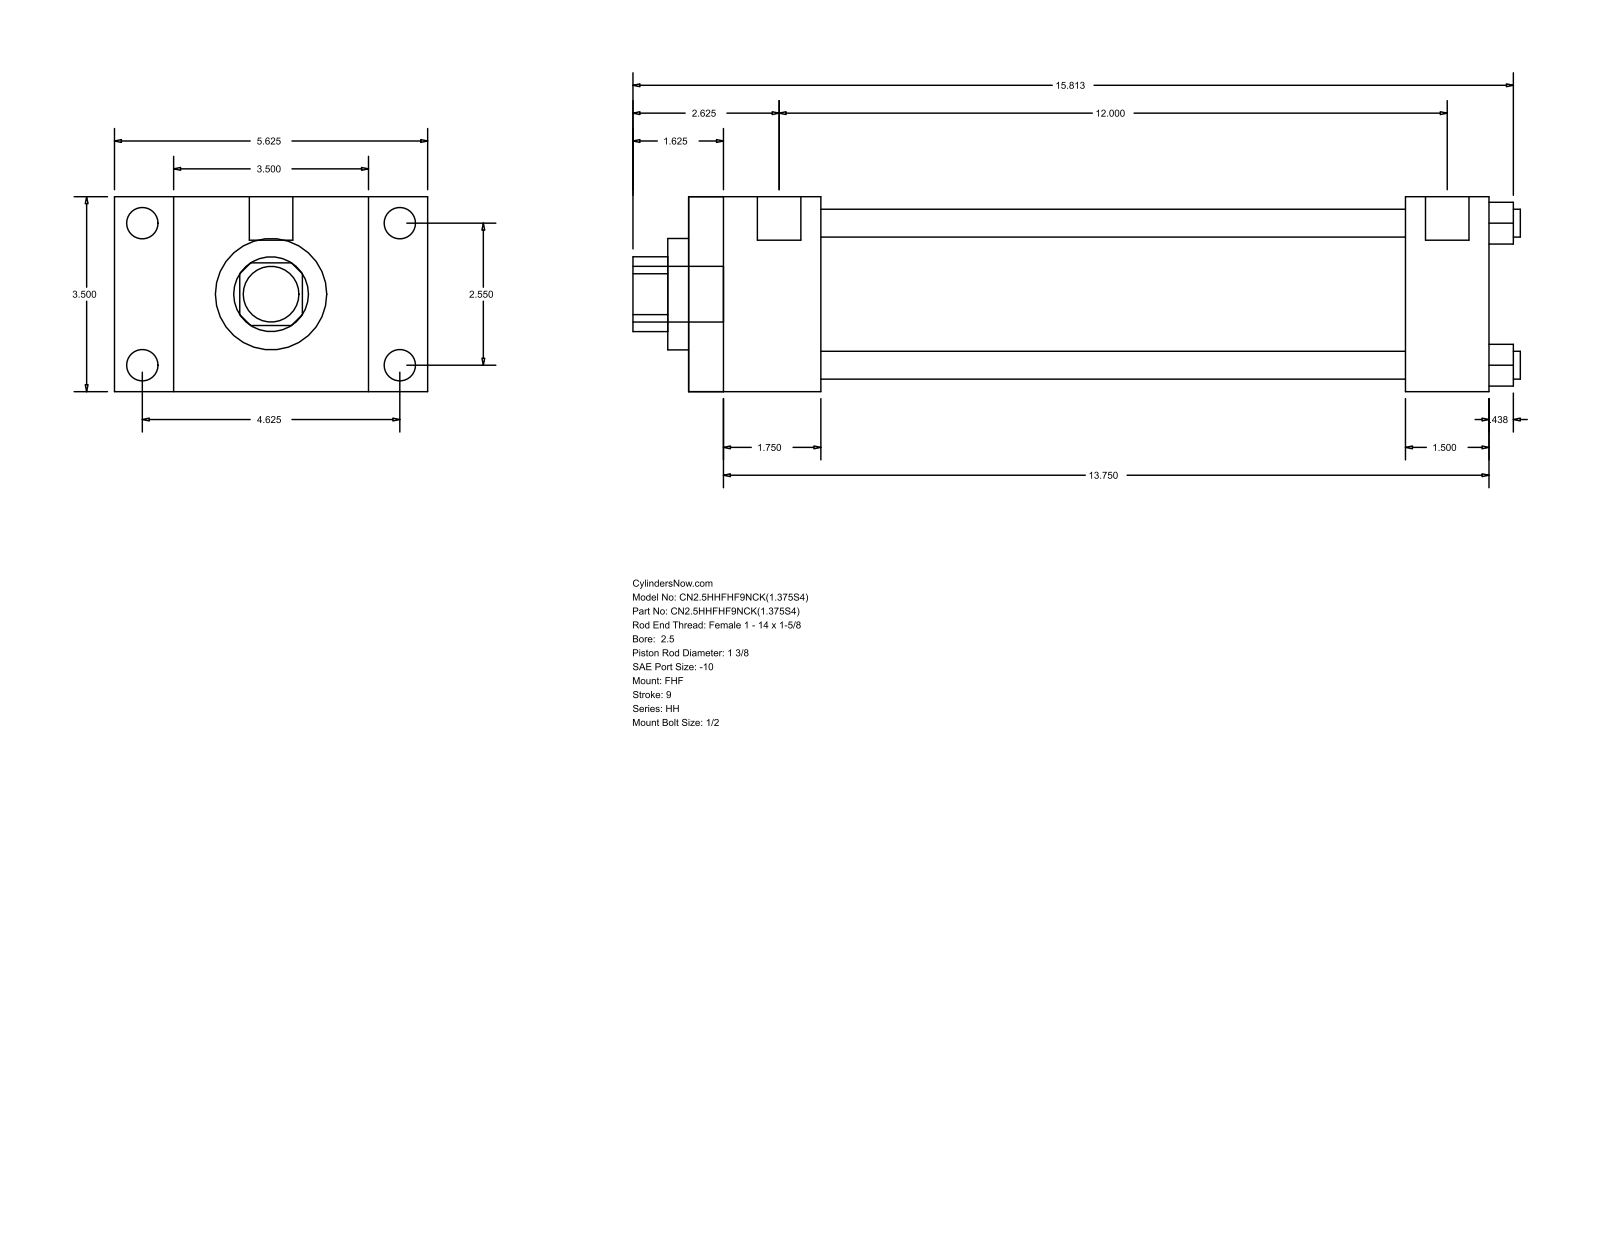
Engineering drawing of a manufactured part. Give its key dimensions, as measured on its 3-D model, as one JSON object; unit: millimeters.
{"part_name": "HH_FHF__0250_1.375", "step_written_by": "GSSL Pune (CONFIG_CONTROL_DESIGN)", "units": "millimeters", "bodies": {"solids": 0, "faces": 88, "planar": 60, "cylindrical": 28, "other": 0}, "overall_size": [404.81, 142.88, 88.9], "round_holes": [[12.7, 4], [34.92, 1], [50.8, 1], [73.03, 1]], "round_bosses_or_shafts": [[14.3, 4], [5.56, 4], [19.84, 2], [25.4, 1]], "partial_cylinders_radius": [[17.06, 1]], "face_to_face_distances": [88.9, 60.32, 26.99, 115.89, 365.12, 304.8, 142.88, 327.03, 266.71, 38.09], "hole_center_spacings": [45.79, 64.76, 91.58]}
